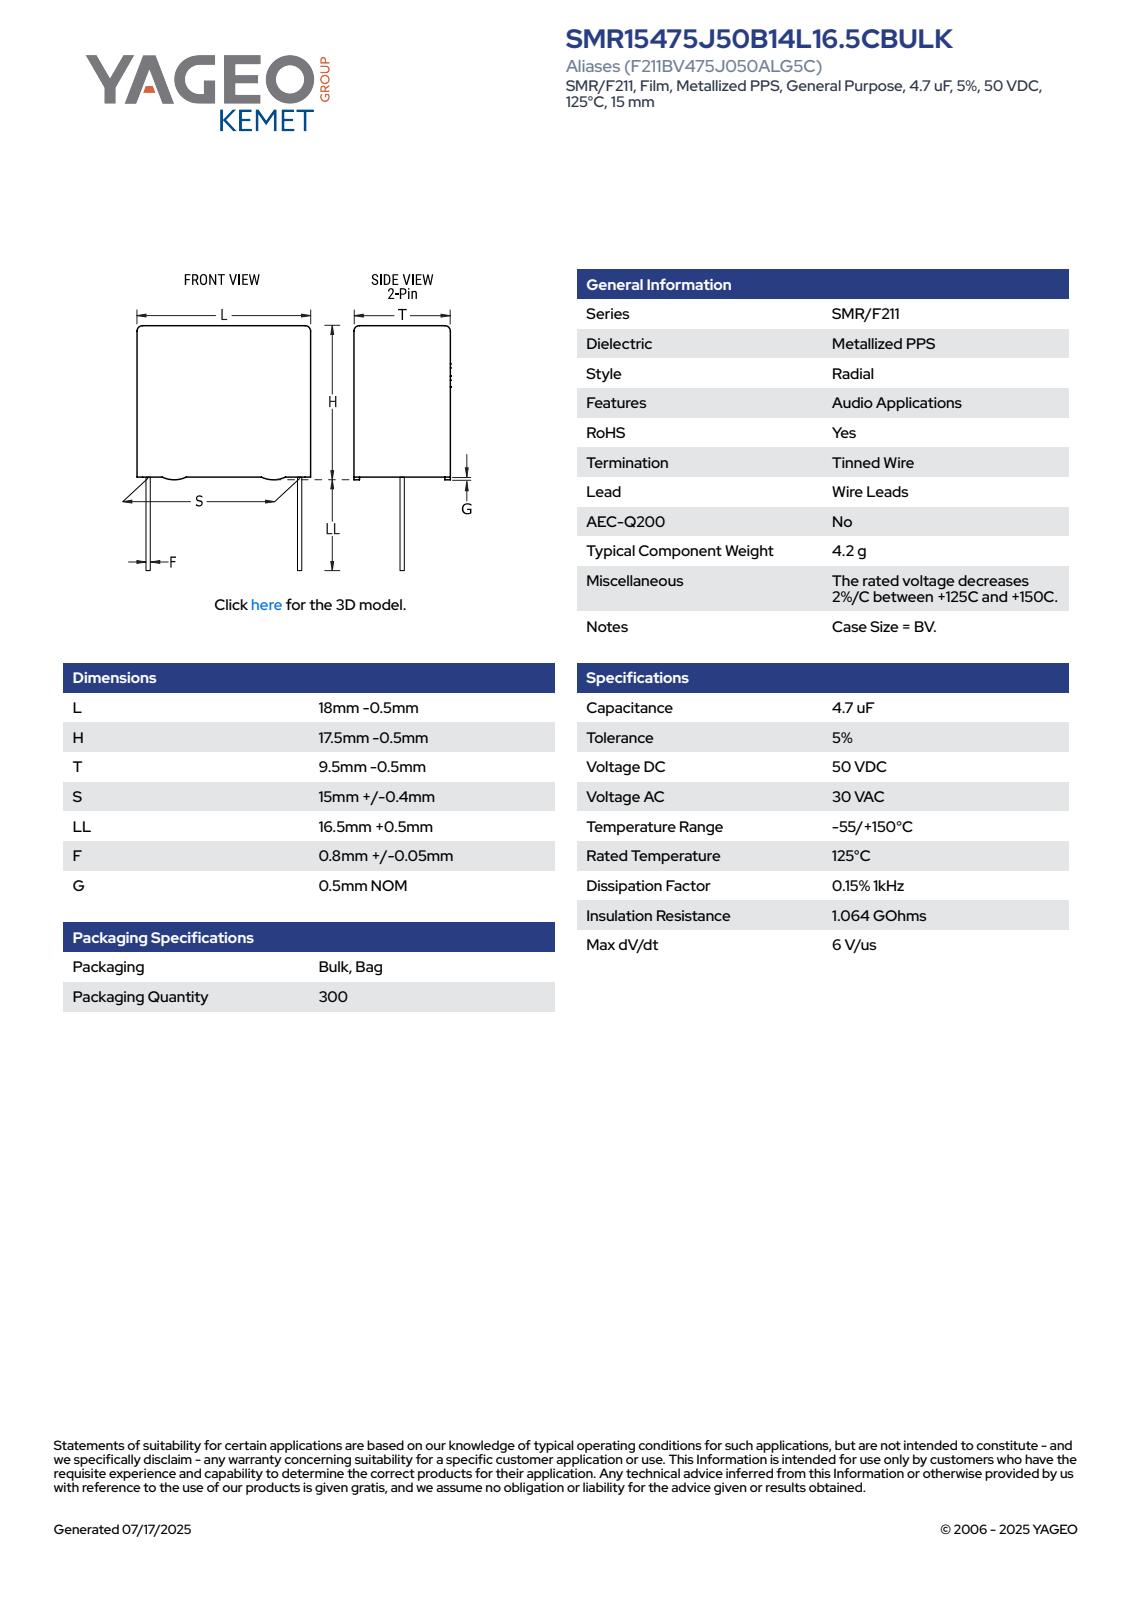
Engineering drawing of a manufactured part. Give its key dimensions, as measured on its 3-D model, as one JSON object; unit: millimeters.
{"part_name": "CFR_RBG_18X17.5X9.5_L17.5H17T9S15LL17F0.85G0.5", "step_written_by": "SolidWorks 2021 (AUTOMOTIVE_DESIGN)", "units": "millimeters", "bodies": {"solids": 4, "faces": 89, "planar": 81, "cylindrical": 8, "other": 0}, "overall_size": [34, 17.5, 9.01], "volume_mm3": 2619, "surface_area_mm2": 1317, "round_bosses_or_shafts": [[0.85, 2]], "partial_cylinders_radius": [[0.5, 4]], "face_to_face_distances": [9, 17.5, 16.5, 17, 0.51, 8.49, 0.5, 7.98, 34, 8.83]}
